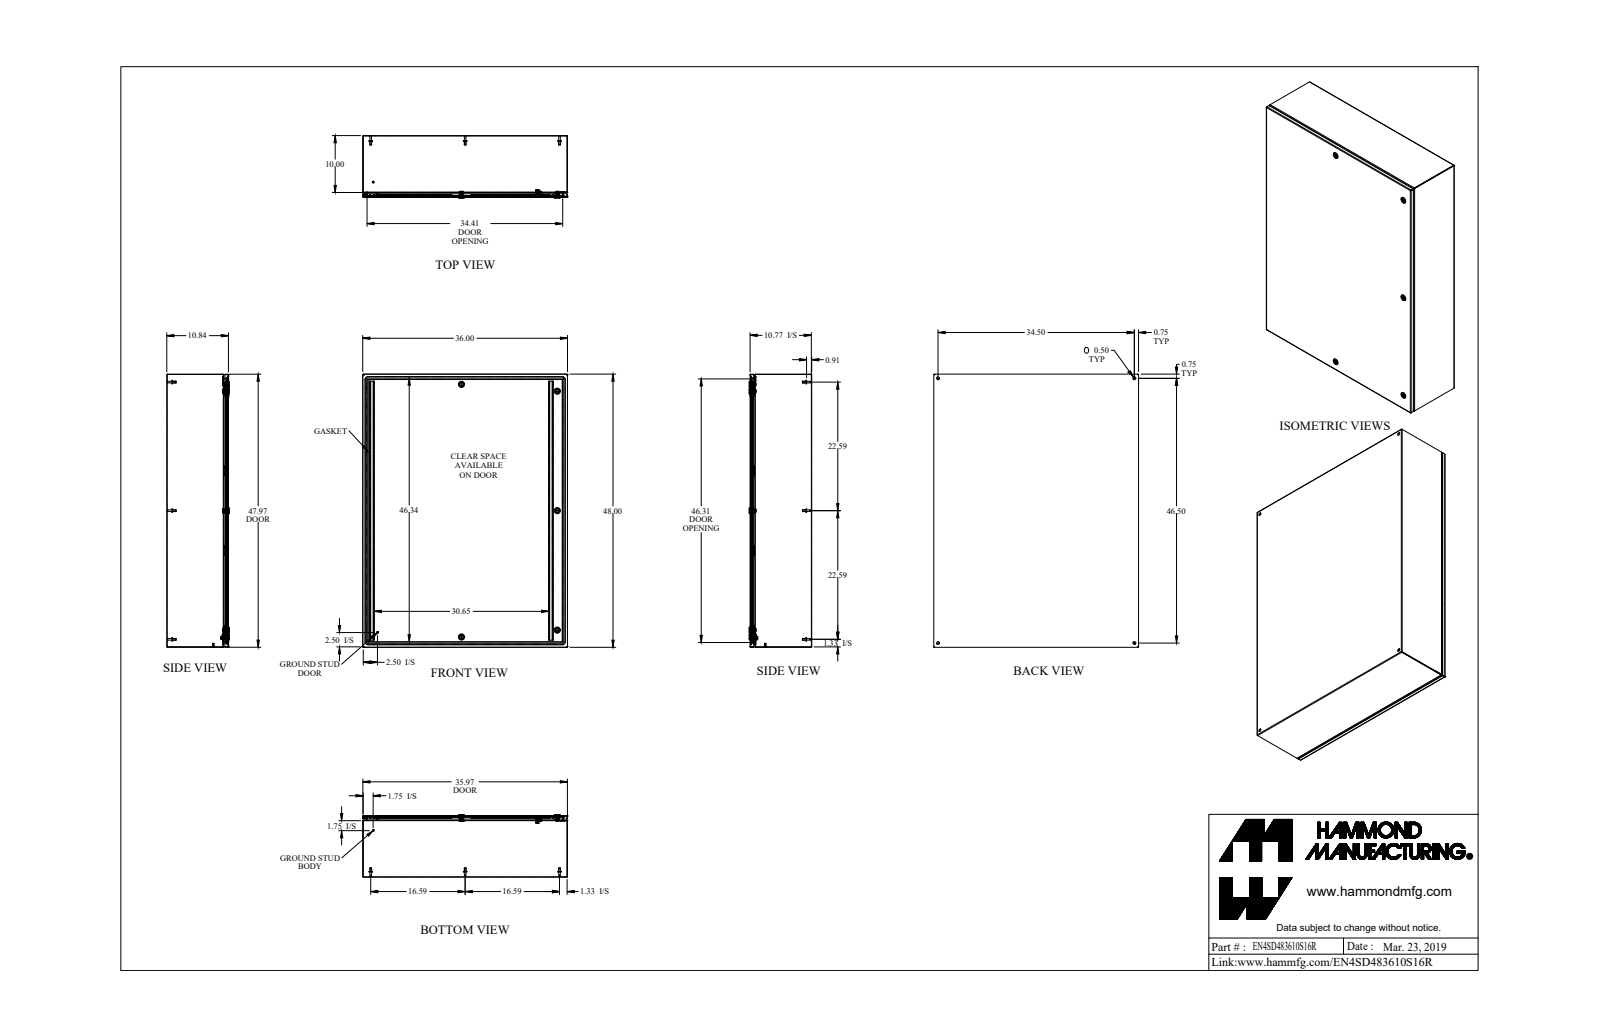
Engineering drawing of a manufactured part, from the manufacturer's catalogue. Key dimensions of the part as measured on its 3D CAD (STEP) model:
Part name (STEP PRODUCT): EN4SD483610S16R
STEP written by: SolidWorks 2018 (AUTOMOTIVE_DESIGN)
Units: inches
Bodies: 64 solids, 1733 faces (896 planar, 552 cylindrical, 285 other)
Overall size (bounding box): 48 × 36 × 11.002
Volume: 424.6 in³ · Surface area: 11 965 in²
Round holes (diameter × count): ⌀0.5 ×9, ⌀0.197 ×5, ⌀0.387 ×5, ⌀0.63 ×5, ⌀0.768 ×5, ⌀0.172 ×1, ⌀0.196 ×1, ⌀0.24 ×1, ⌀0.242 ×1, ⌀0.275 ×1, ⌀0.375 ×1
Round bosses / shafts (diameter × count): ⌀0.625 ×11, ⌀0.313 ×10, ⌀0.275 ×8, ⌀1.1 ×5, ⌀0.236 ×5, ⌀0.785 ×3, ⌀0.625 ×3, ⌀0.525 ×3
Partial cylindrical surfaces — rounded edges, fillets, slot ends (radius × count): R0.01 ×24, R0.048 ×24, R0.036 ×20, R0.108 ×20, R0.062 ×17, R0.094 ×10, R0.125 ×10, R0.016 ×9
Main face-to-face distances: 0.072, 10.77, 10.698, 10.842, 35.928, 35.856, 36, 0.072, 48, 47.928
Hole centre spacings: 16.634, 16.881, 17.931, 23.274, 27.854, 33.516, 34.5, 40.728
